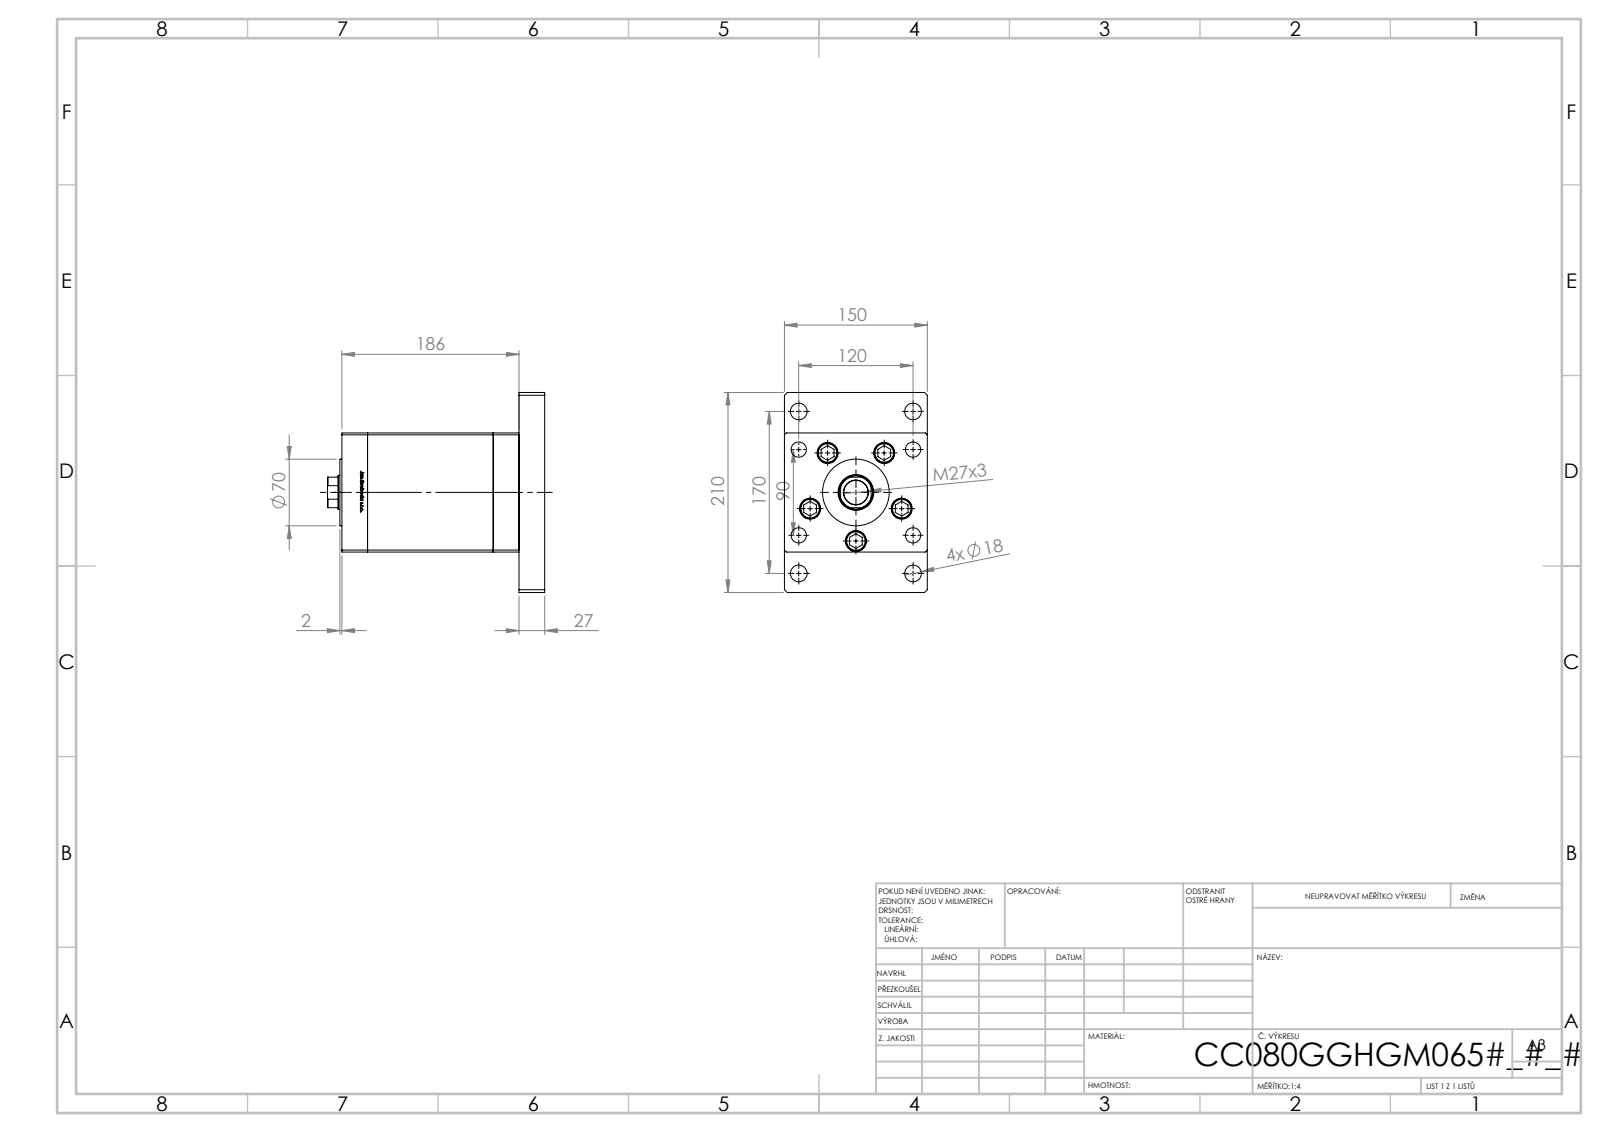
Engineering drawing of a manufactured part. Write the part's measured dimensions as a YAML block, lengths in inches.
part_name: "V220C_VC_G; V220C_FRONT_G; ALLEN BOLT; V220C_F (+2 more)"
step_written_by: "SolidWorks 2019 (CONFIG_CONTROL_DESIGN)"
units: inches
bodies: {solids: 19, faces: 1313, planar: 518, cylindrical: 189, other: 606}
overall_size: [8.976, 8.268, 5.906]
volume: 233.5
surface_area: 674.8
round_holes:
  - {diameter: 0.63, count: 9}
  - {diameter: 0.689, count: 9}
  - {diameter: 0.866, count: 5}
  - {diameter: 0.827, count: 4}
  - {diameter: 0.079, count: 2}
  - {diameter: 0.518, count: 2}
  - {diameter: 1.004, count: 1}
  - {diameter: 1.417, count: 1}
  - {diameter: 1.476, count: 1}
  - {diameter: 4.016, count: 1}
round_bosses_or_shafts:
  - {diameter: 0.315, count: 9}
  - {diameter: 0.827, count: 5}
  - {diameter: 3.15, count: 1}
  - {diameter: 2.756, count: 1}
partial_cylinders:
  - {radius: 0.037, count: 2}
  - {radius: 0.689, count: 1}
face_to_face_distances: [1.063, 6.26, 7.323, 5.906, 5.197, 2.126, 4.921, 0.079, 8.386, 7.244]
hole_center_spacings: [2.008, 1.575, 2.953, 4.096, 4.724, 4.98, 5.118, 6.965]
